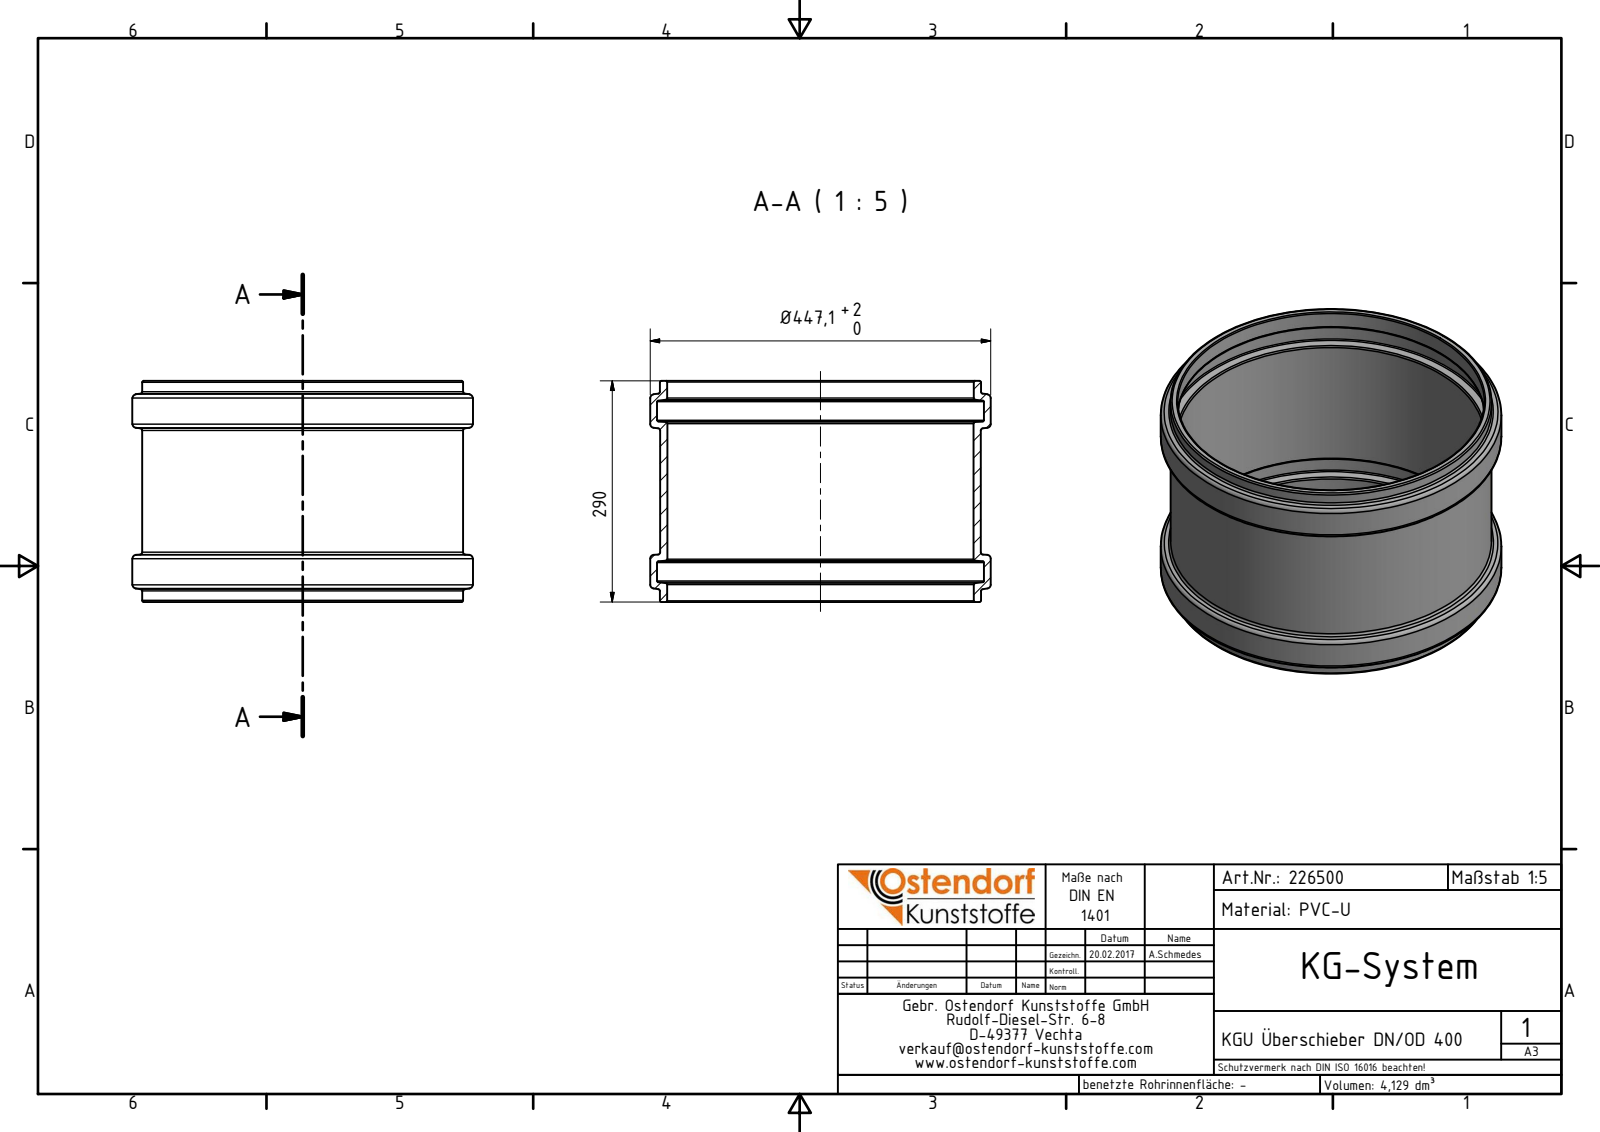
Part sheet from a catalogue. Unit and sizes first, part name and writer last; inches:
Units: inches
Overall size (bounding box): 17.602 × 17.602 × 12.835
Round holes (diameter × count): ⌀15.827 ×1, ⌀15.843 ×1, ⌀16.894 ×1
Round bosses / shafts (diameter × count): ⌀17.602 ×1, ⌀16.591 ×1, ⌀16.579 ×1
Main face-to-face distances: 12.835
Volume: 279.1 in³ · Surface area: 1 522 in²
Bodies: 1 solid, 40 faces (2 planar, 10 cylindrical, 28 other)
Part name (STEP PRODUCT): 226500 KGU Überschiebmuffe DN_OD 400
STEP written by: Autodesk Inventor 2016 (AUTOMOTIVE_DESIGN)
